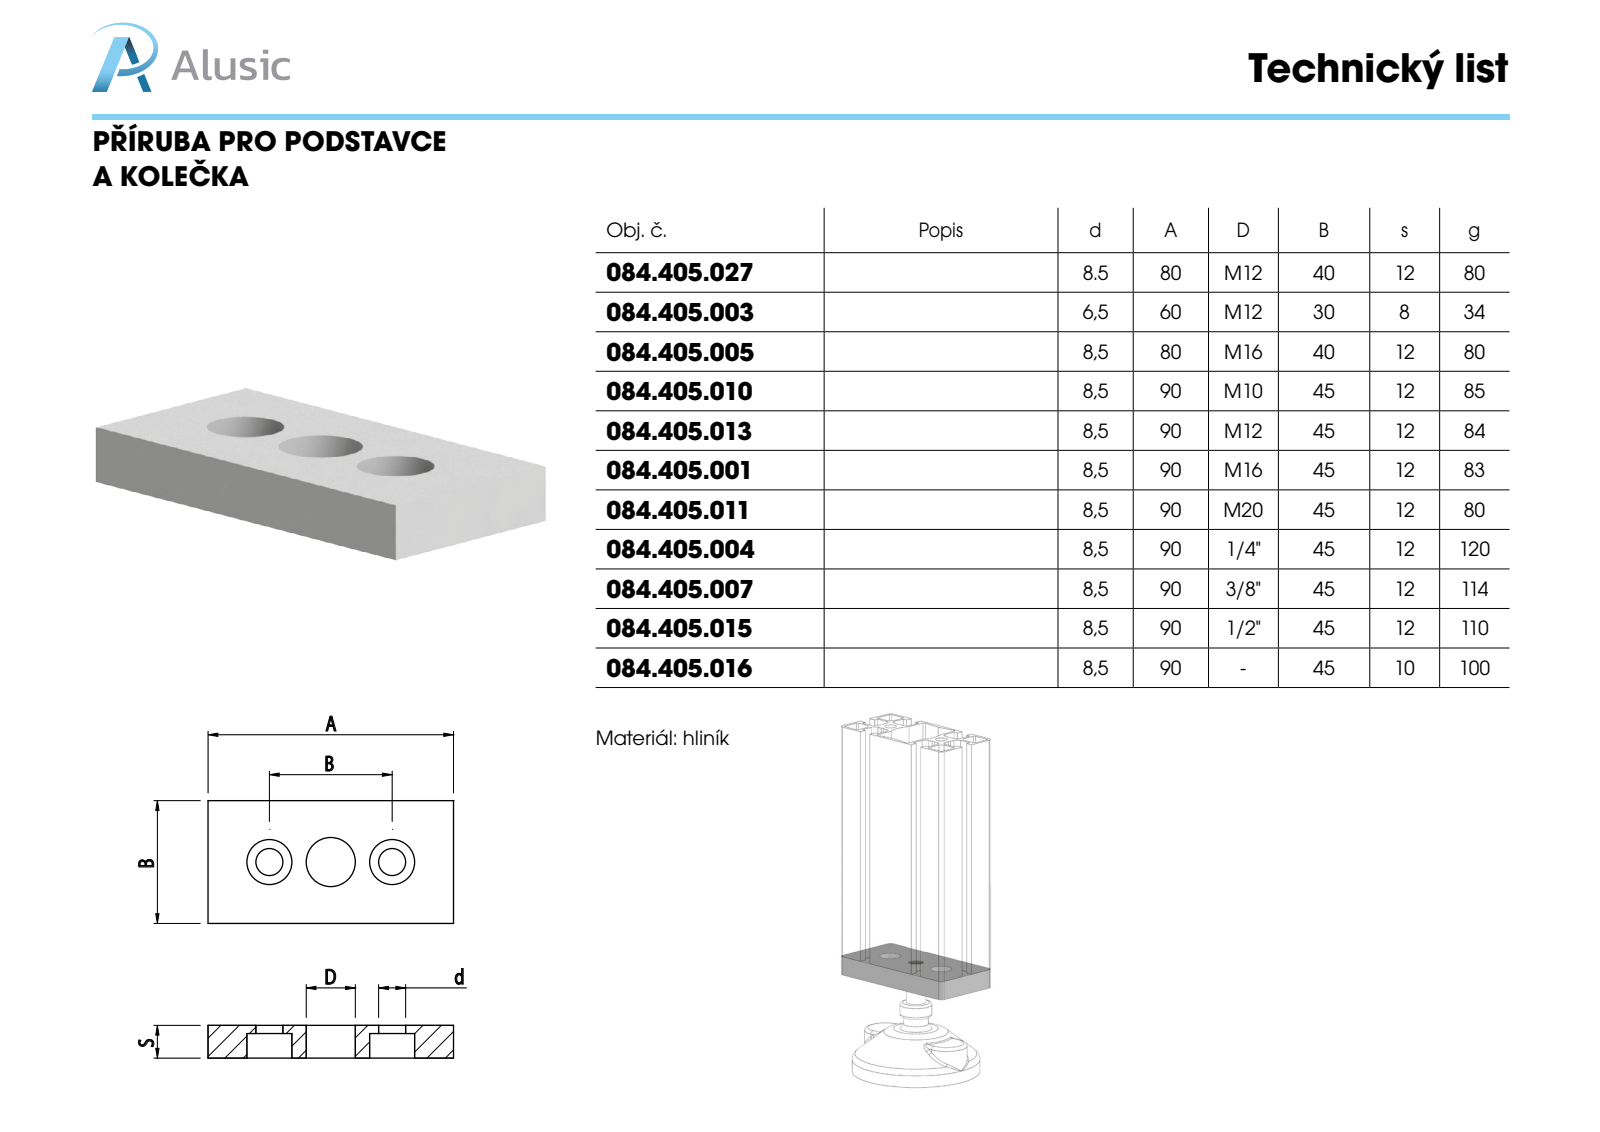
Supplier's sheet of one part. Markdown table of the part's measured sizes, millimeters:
| quantity | value |
| --- | --- |
| part name | 084.405.004 |
| STEP written by | SolidWorks 2011 (CONFIG_CONTROL_DESIGN) |
| units | millimeters |
| bodies | 1 solid, 22 faces (8 planar, 14 cylindrical, 0 other) |
| overall size | 90 × 45 × 12 |
| volume | 44 822 mm³ |
| surface area | 12 084 mm² |
| round holes (diameter × count) | 9 × 2, 13.5 × 2, 11.8 × 1 |
| partial cylindrical surfaces (radius × count) | 2.5 × 4 |
| main face-to-face distances | 12, 45, 90, 6.5, 5.5 |
| hole center spacings | 22.5, 45 |
